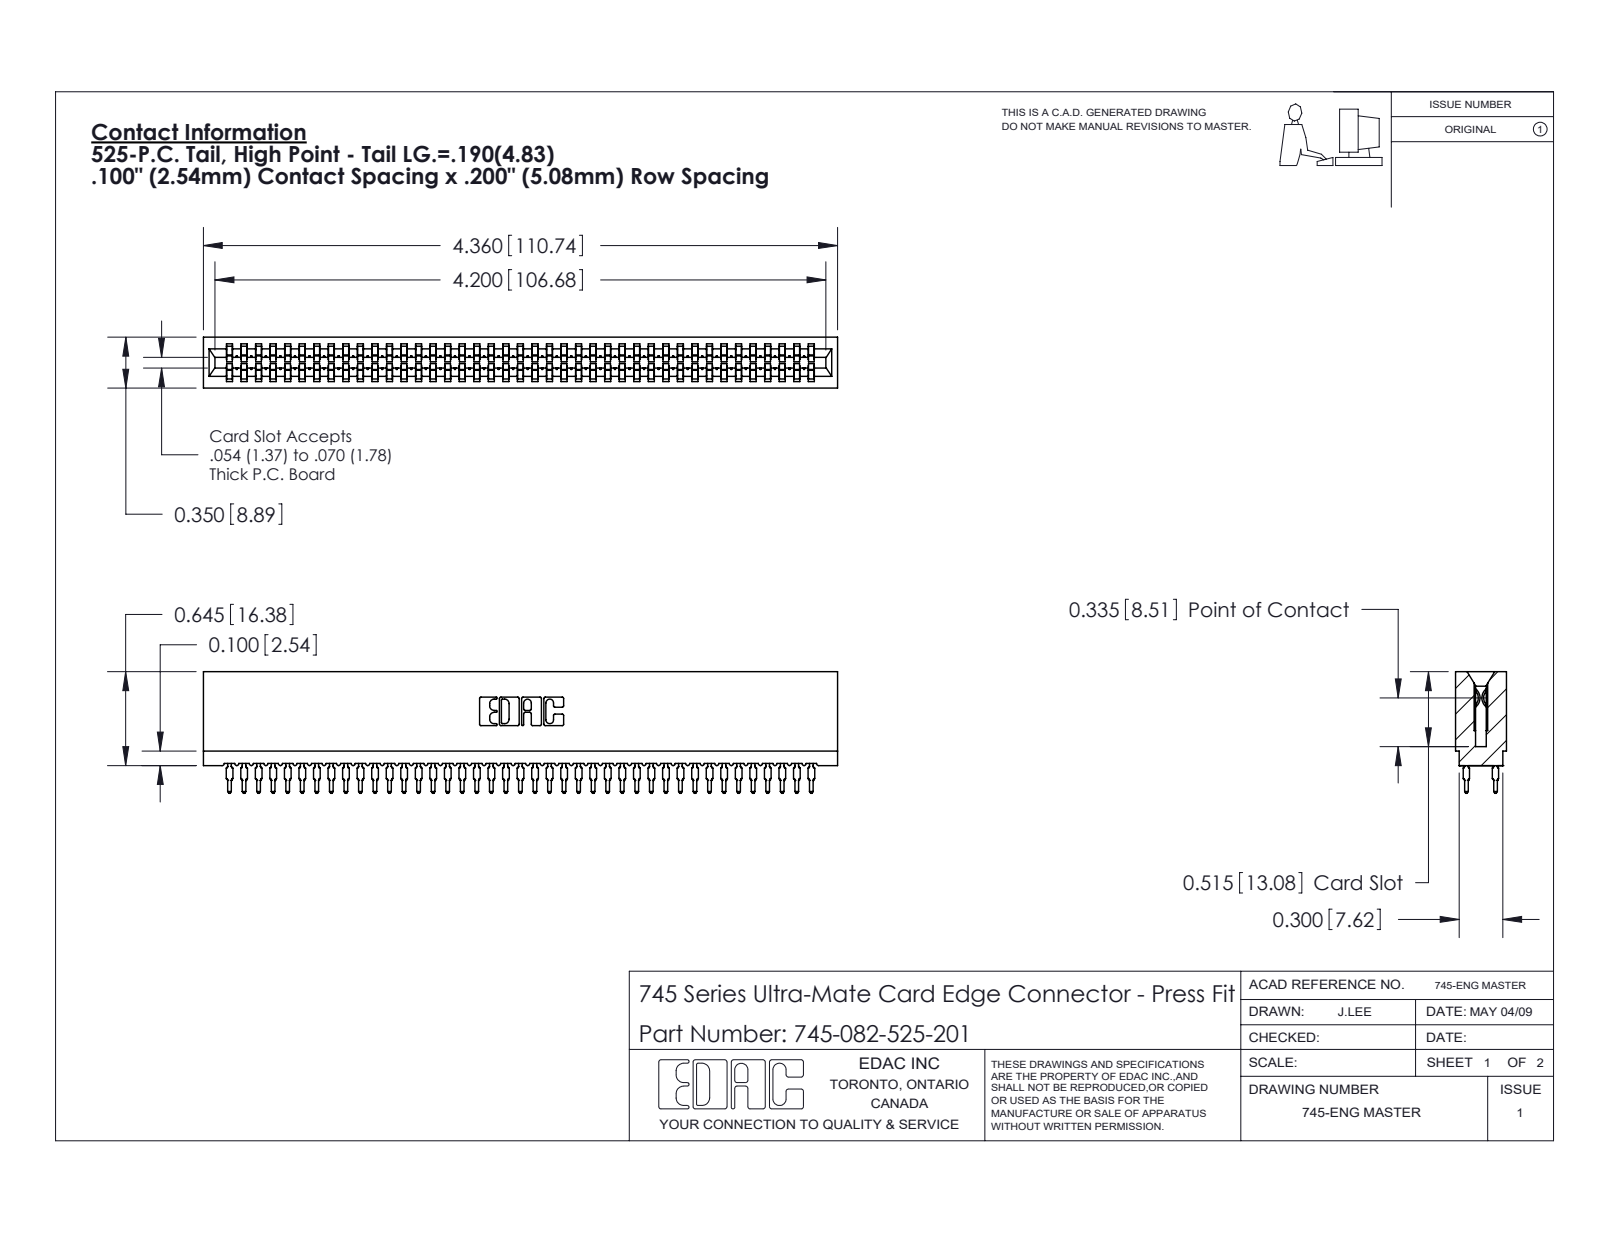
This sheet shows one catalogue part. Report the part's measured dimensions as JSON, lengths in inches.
{"part_name": "745-292-001_525; 745-082-525-201; 745 Part_Insulator Option - 01", "step_written_by": "SolidWorks 2020 (CONFIG_CONTROL_DESIGN)", "units": "inches", "bodies": {"solids": 83, "faces": 7434, "planar": 3827, "cylindrical": 1475, "other": 2132}, "overall_size": [4.36, 0.836, 0.35], "volume_in3": 0.608, "surface_area_in2": 31.22, "partial_cylinders_radius": [[0.021, 164], [0.015, 82], [0.01, 22], [0.005, 8], [0.011, 8], [0.007, 6], [0.031, 6], [0.026, 3]], "face_to_face_distances": [0.35, 0.063, 0.287, 0.138, 0.212, 0.076, 0.149, 0.045, 0.305, 0.018]}
